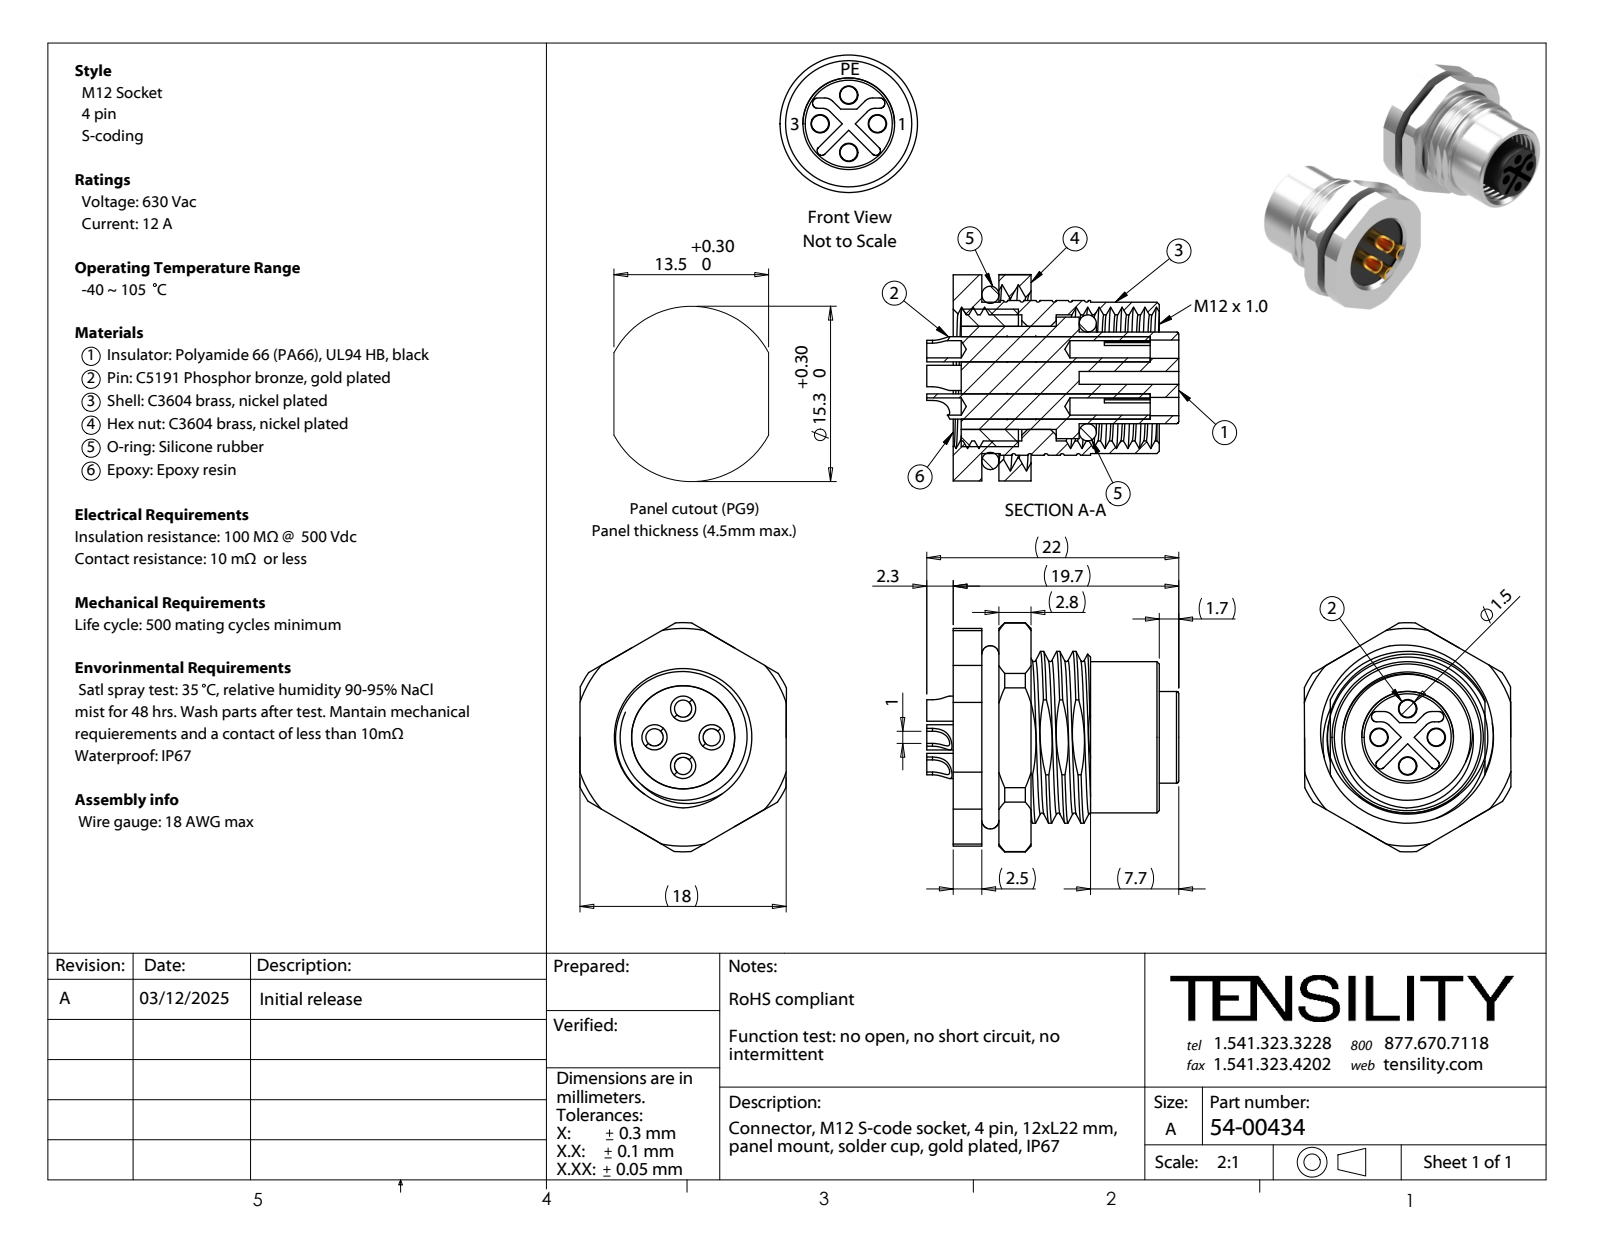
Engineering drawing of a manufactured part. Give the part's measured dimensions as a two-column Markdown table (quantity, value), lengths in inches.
| quantity | value |
| --- | --- |
| part name | 54-00434-06; 54-00434-05; 54-00434-04; 54-00434-02 (+3 more) |
| STEP written by | SolidWorks 2021 (CONFIG_CONTROL_DESIGN) |
| units | inches |
| bodies | 10 solids, 336 faces (112 planar, 137 cylindrical, 87 other) |
| overall size | 0.866 × 0.787 × 0.71 |
| volume | 0.174 in³ |
| surface area | 9.125 in² |
| round holes (diameter × count) | 0.059 × 4, 0.063 × 4, 0.354 × 1, 0.433 × 1, 0.551 × 1 |
| round bosses / shafts (diameter × count) | 0.087 × 4, 0.52 × 1, 0.472 × 1, 0.417 × 1, 0.315 × 1 |
| partial cylindrical surfaces (radius × count) | 0.039 × 4, 0.016 × 2, 0.018 × 2, 0.073 × 2, 0.295 × 1, 0.374 × 1, 0.394 × 1 |
| main face-to-face distances | 0.098, 0.709, 0.13, 0.197, 0.028, 0.071, 0.031, 0.157, 0.169, 0.059 |
| hole center spacings | 0.098, 0.139, 0.197 |
